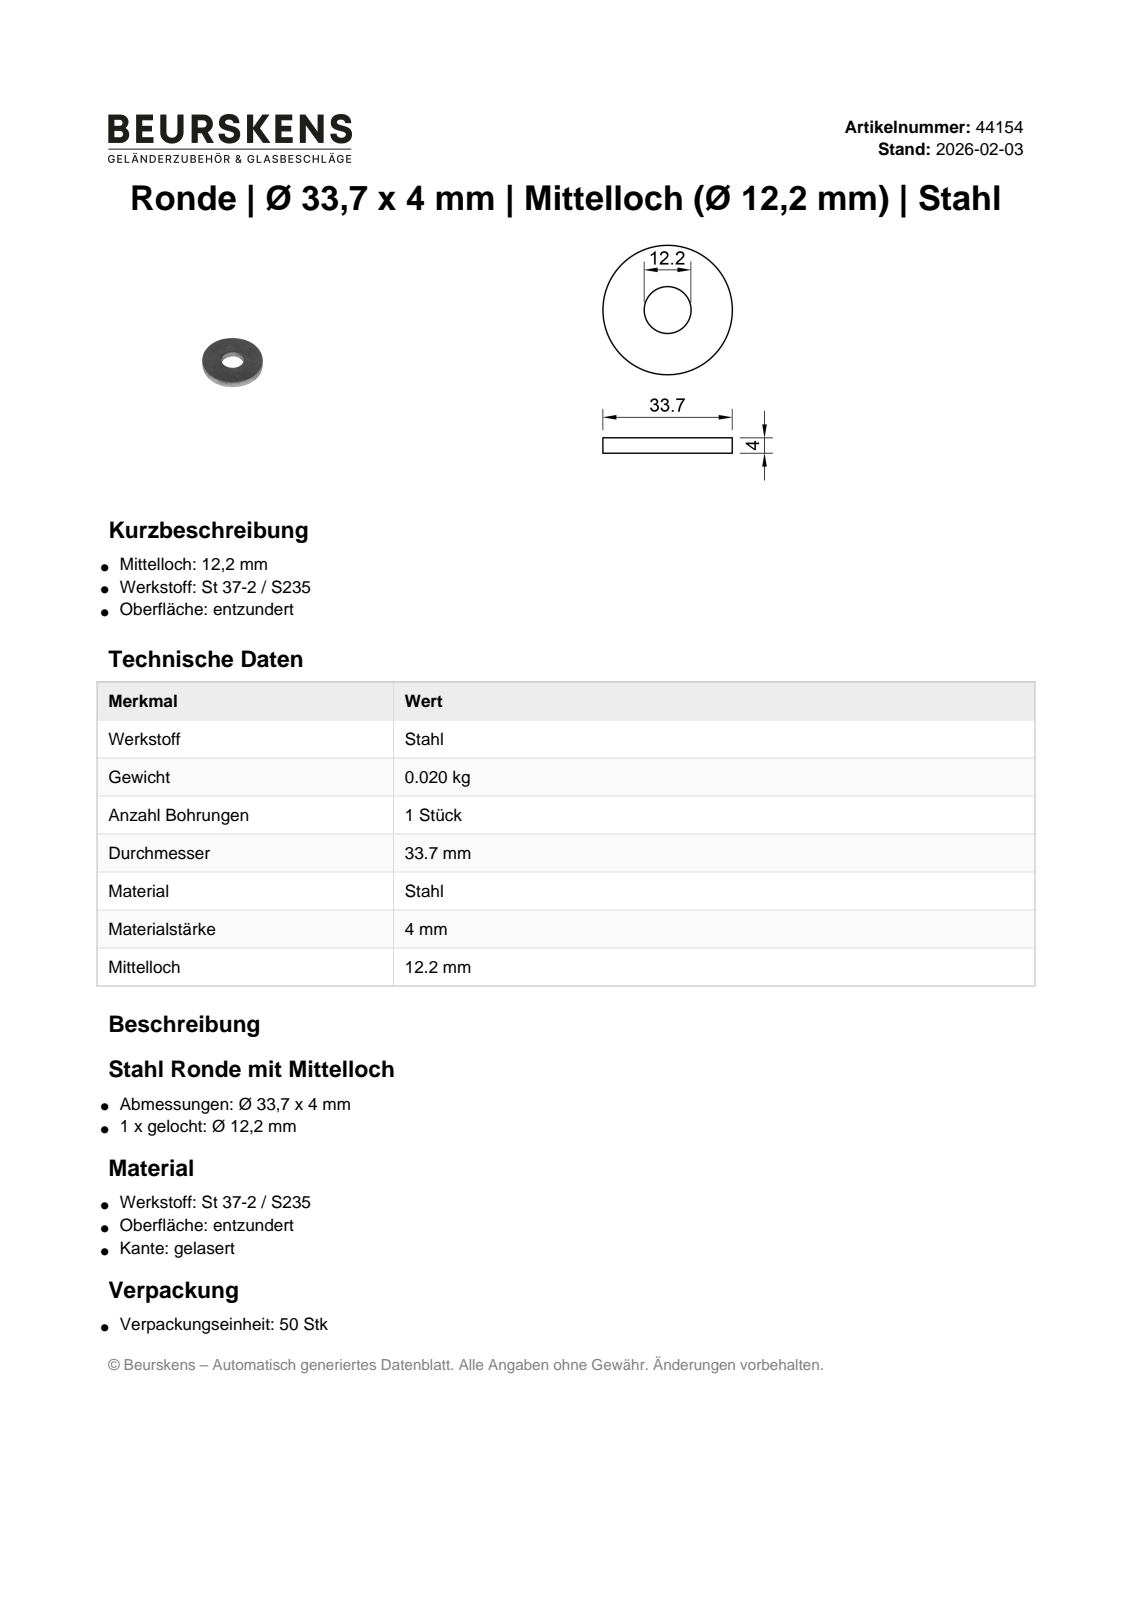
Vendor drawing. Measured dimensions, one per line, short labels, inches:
name: 44154
written by: Autodesk Inventor 2023 (AUTOMOTIVE_DESIGN)
unit: in
bodies: 1 solid, 4 faces (2 planar, 2 cylindrical, 0 other)
size: 1.327 × 1.327 × 0.157
volume: 0.189 in³; area: 3.297 in²
holes: 1× ⌀0.48
bosses: 1× ⌀1.327
face distances: 0.157
